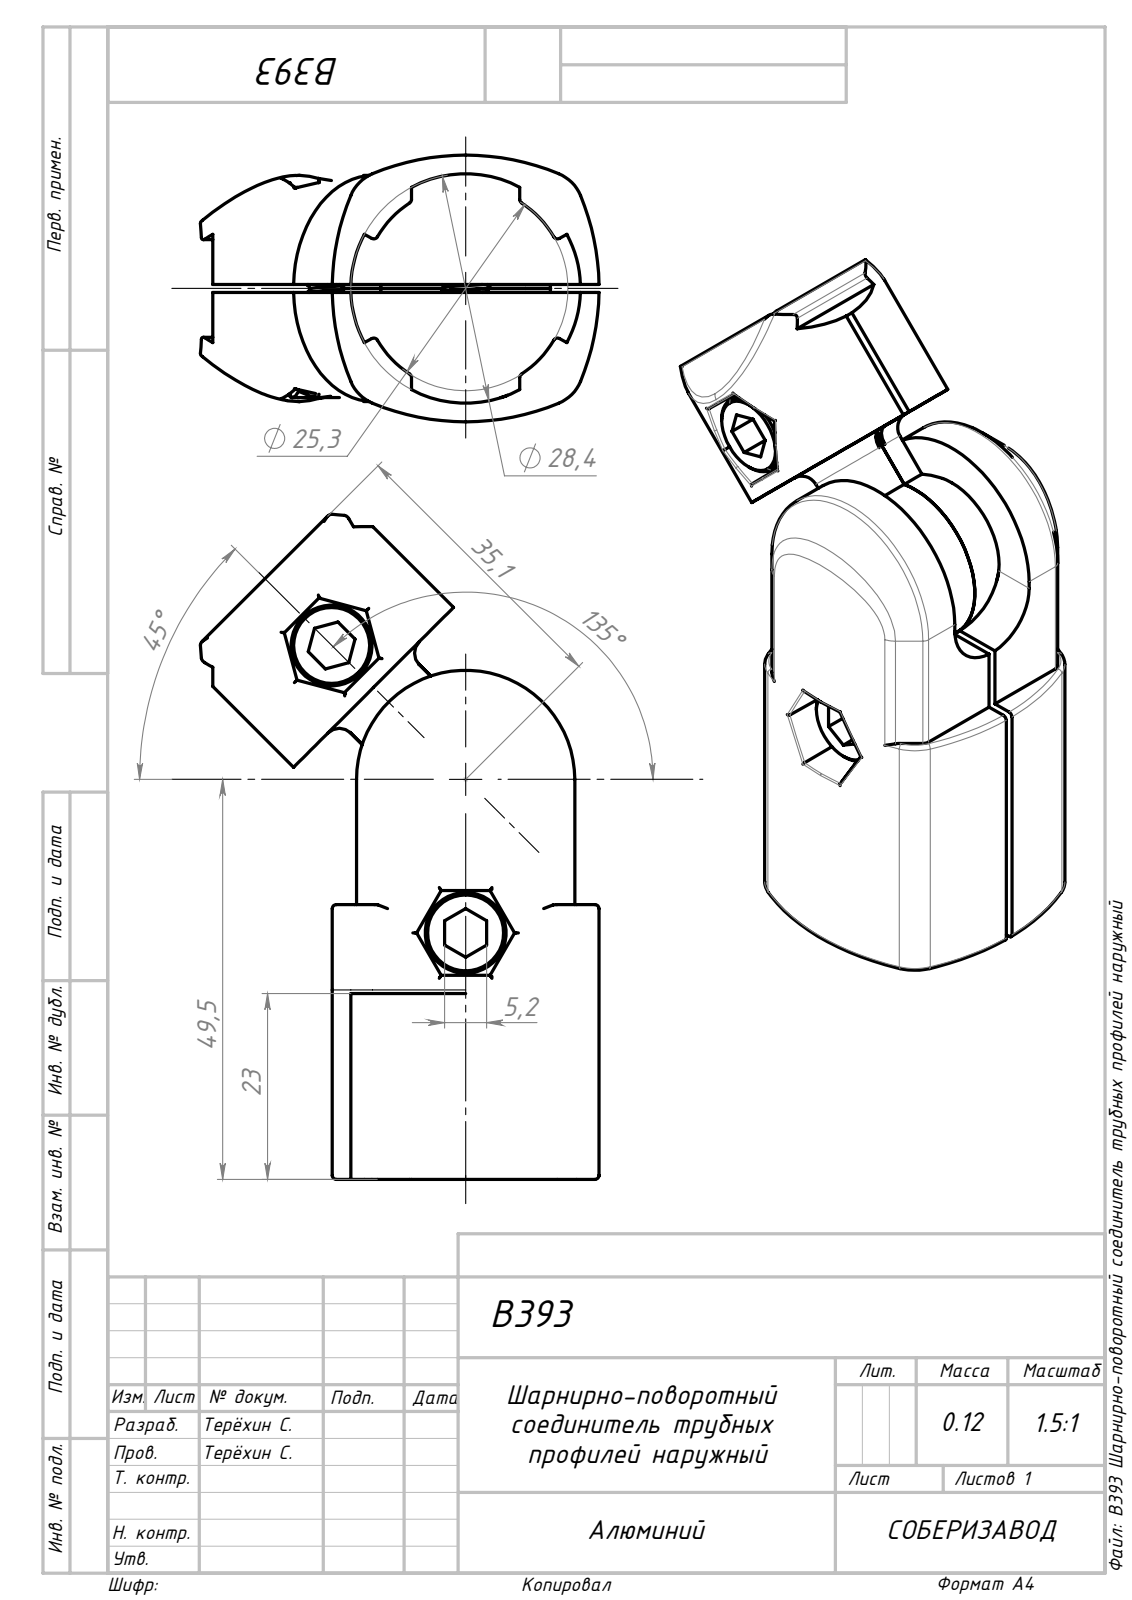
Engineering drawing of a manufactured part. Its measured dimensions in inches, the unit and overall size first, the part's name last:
Units: inches
Overall size (bounding box): 3.211 × 2.38 × 1.299
Round holes (diameter × count): ⌀0.205 ×2, ⌀0.256 ×2, ⌀1.118 ×1
Round bosses / shafts (diameter × count): ⌀0.394 ×2, ⌀0.236 ×2, ⌀1.102 ×1, ⌀0.472 ×1
Partial cylindrical surfaces — rounded edges, fillets, slot ends (radius × count): R0.02 ×70, R0.039 ×4, R0.118 ×4, R0.197 ×4, R1.181 ×4, R0.256 ×2, R0.472 ×1, R0.49 ×1
Main face-to-face distances: 0.02, 0.276, 0.236, 0.039, 0.256, 0.512, 0.405, 0.394, 0.118, 0.354
Hole centre spacings: 1.545
Volume: 2.572 in³ · Surface area: 36.85 in²
Bodies: 8 solids, 648 faces (202 planar, 226 cylindrical, 220 other)
Part name (STEP PRODUCT): B393 Шарнирно-поворотный соединитель трубных профилей наружный
STEP written by: SolidWorks 2022 (AUTOMOTIVE_DESIGN)
